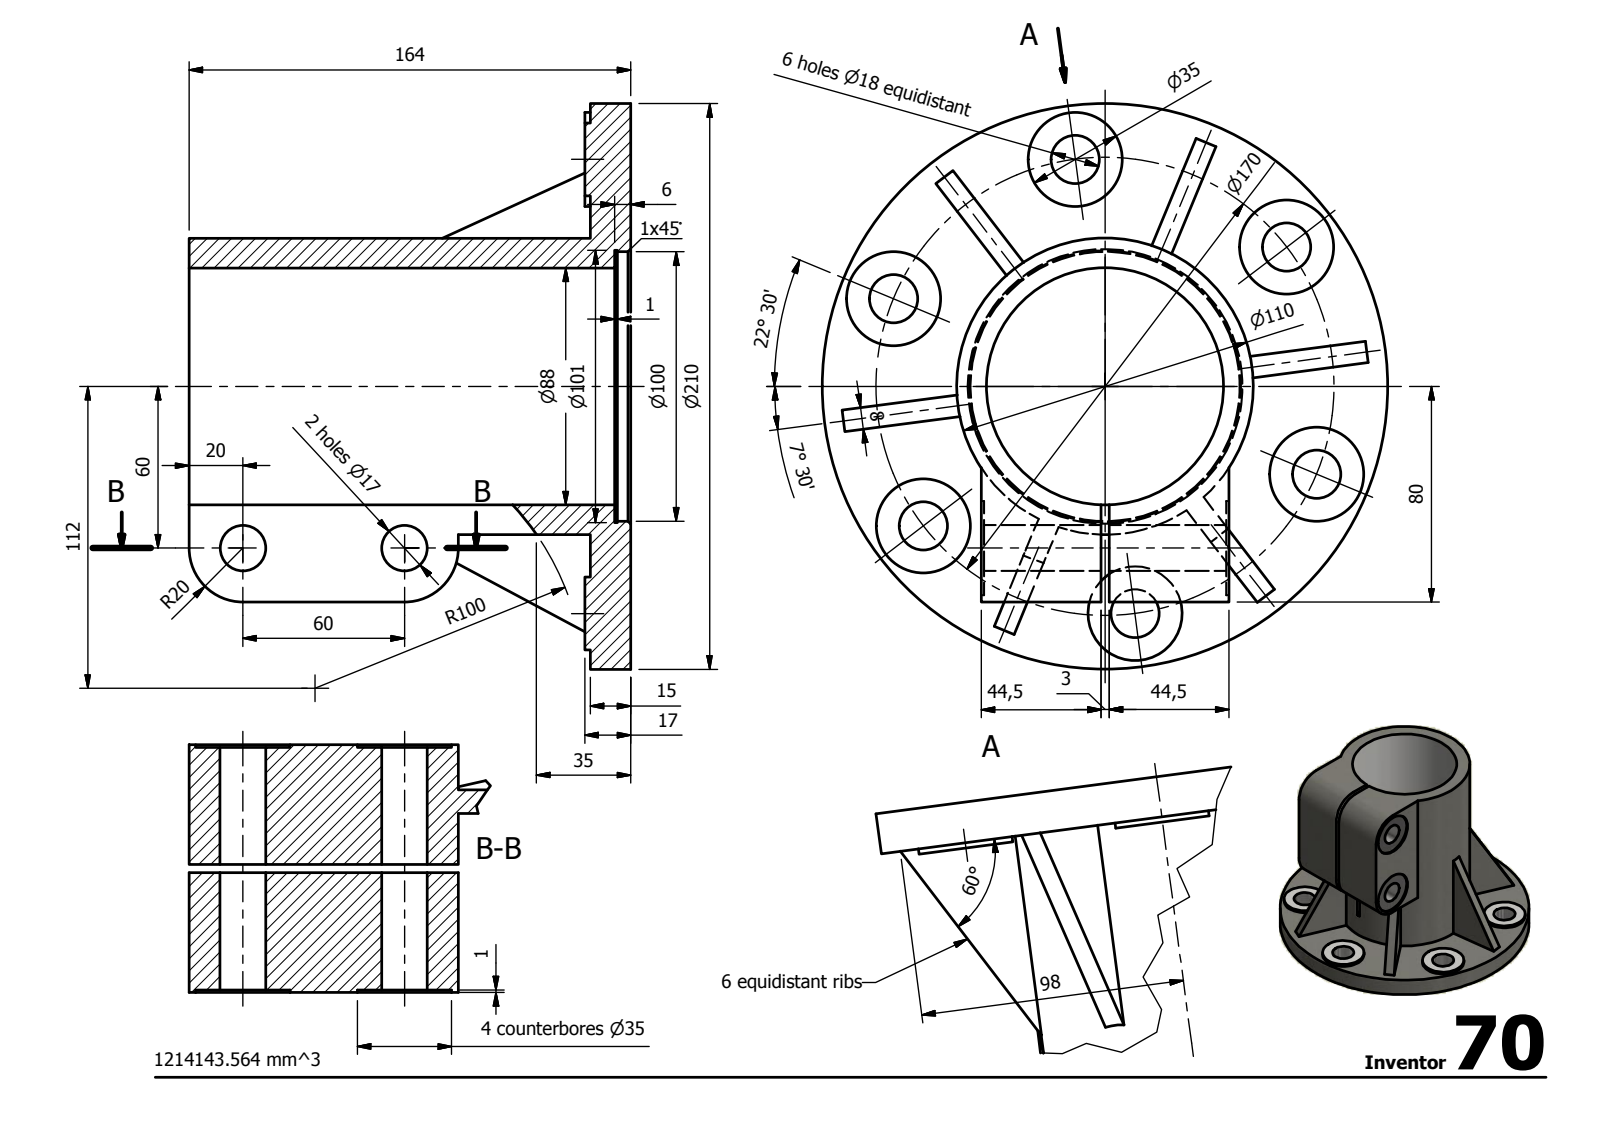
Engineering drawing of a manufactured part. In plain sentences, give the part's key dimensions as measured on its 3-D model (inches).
Its 3-D file was written by "Autodesk Inventor 2014 (AUTOMOTIVE_DESIGN)". It is 1 solid with 74 faces: 42 planar, 31 cylindrical and 1 other. Overall it measures 8.268 by 8.268 by 6.457 inches. Its volume is 74.08 cubic inches and its surface area 328.3 square inches. Round holes: 6 of diameter 0.709, 2 of diameter 0.669, 2 of diameter 1.378, 1 of diameter 3.465, 1 of diameter 3.937, 1 of diameter 3.976. Round bosses or shafts: 6 of diameter 1.378, 1 of diameter 8.268, 1 of diameter 4.331. Partial cylindrical surfaces (rounded edges, fillets, slot ends): 2 of radius 0.787, 1 of radius 3.937. The main face-to-face distances are 0.591, 1.752, 1.87, 6.457, 5.866, 0.669, 0.079, 5.787, 0.118, 0.315. The hole center spacings are 3.346, 5.796, 5.796, 6.693, 2.362, 6.693.
